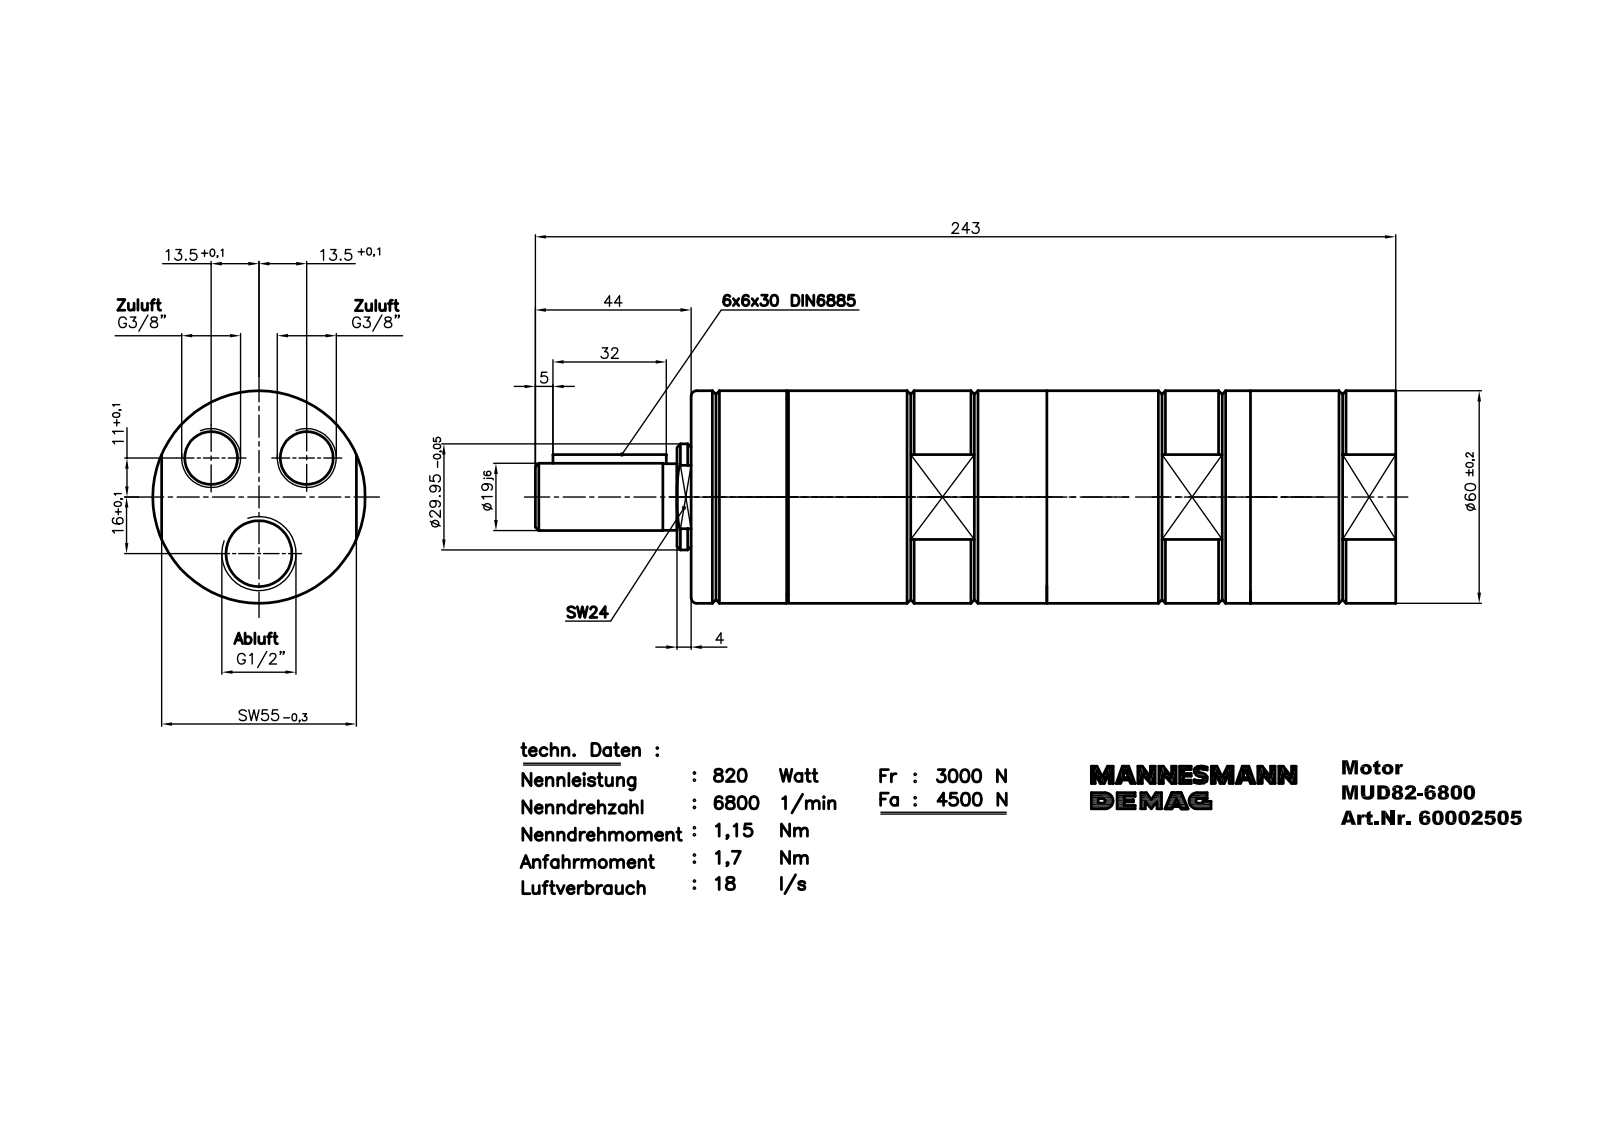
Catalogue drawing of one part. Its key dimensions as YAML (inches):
part_name: "MUD 82-6800_60002505"
step_written_by: "Autodesk Inventor 2008 (CONFIG_CONTROL_DESIGN)"
units: inches
bodies: {solids: 1, faces: 185, planar: 104, cylindrical: 36, other: 45}
overall_size: [9.567, 2.362, 2.362]
volume: 34.07
surface_area: 79.62
round_holes:
  - {diameter: 0.061, count: 1}
  - {diameter: 0.157, count: 1}
  - {diameter: 0.217, count: 1}
  - {diameter: 1.378, count: 1}
round_bosses_or_shafts:
  - {diameter: 2.362, count: 1}
  - {diameter: 2.279, count: 1}
  - {diameter: 1.179, count: 1}
  - {diameter: 0.748, count: 1}
  - {diameter: 0.74, count: 1}
  - {diameter: 0.197, count: 1}
  - {diameter: 0.142, count: 1}
partial_cylinders:
  - {radius: 0.118, count: 2}
  - {radius: 0.295, count: 2}
  - {radius: 0.335, count: 1}
  - {radius: 0.925, count: 1}
  - {radius: 1.057, count: 1}
face_to_face_distances: [7.835, 2.165, 7.173, 0.662, 7.323, 0.15, 0.512, 0.157, 7.33, 7.48]
